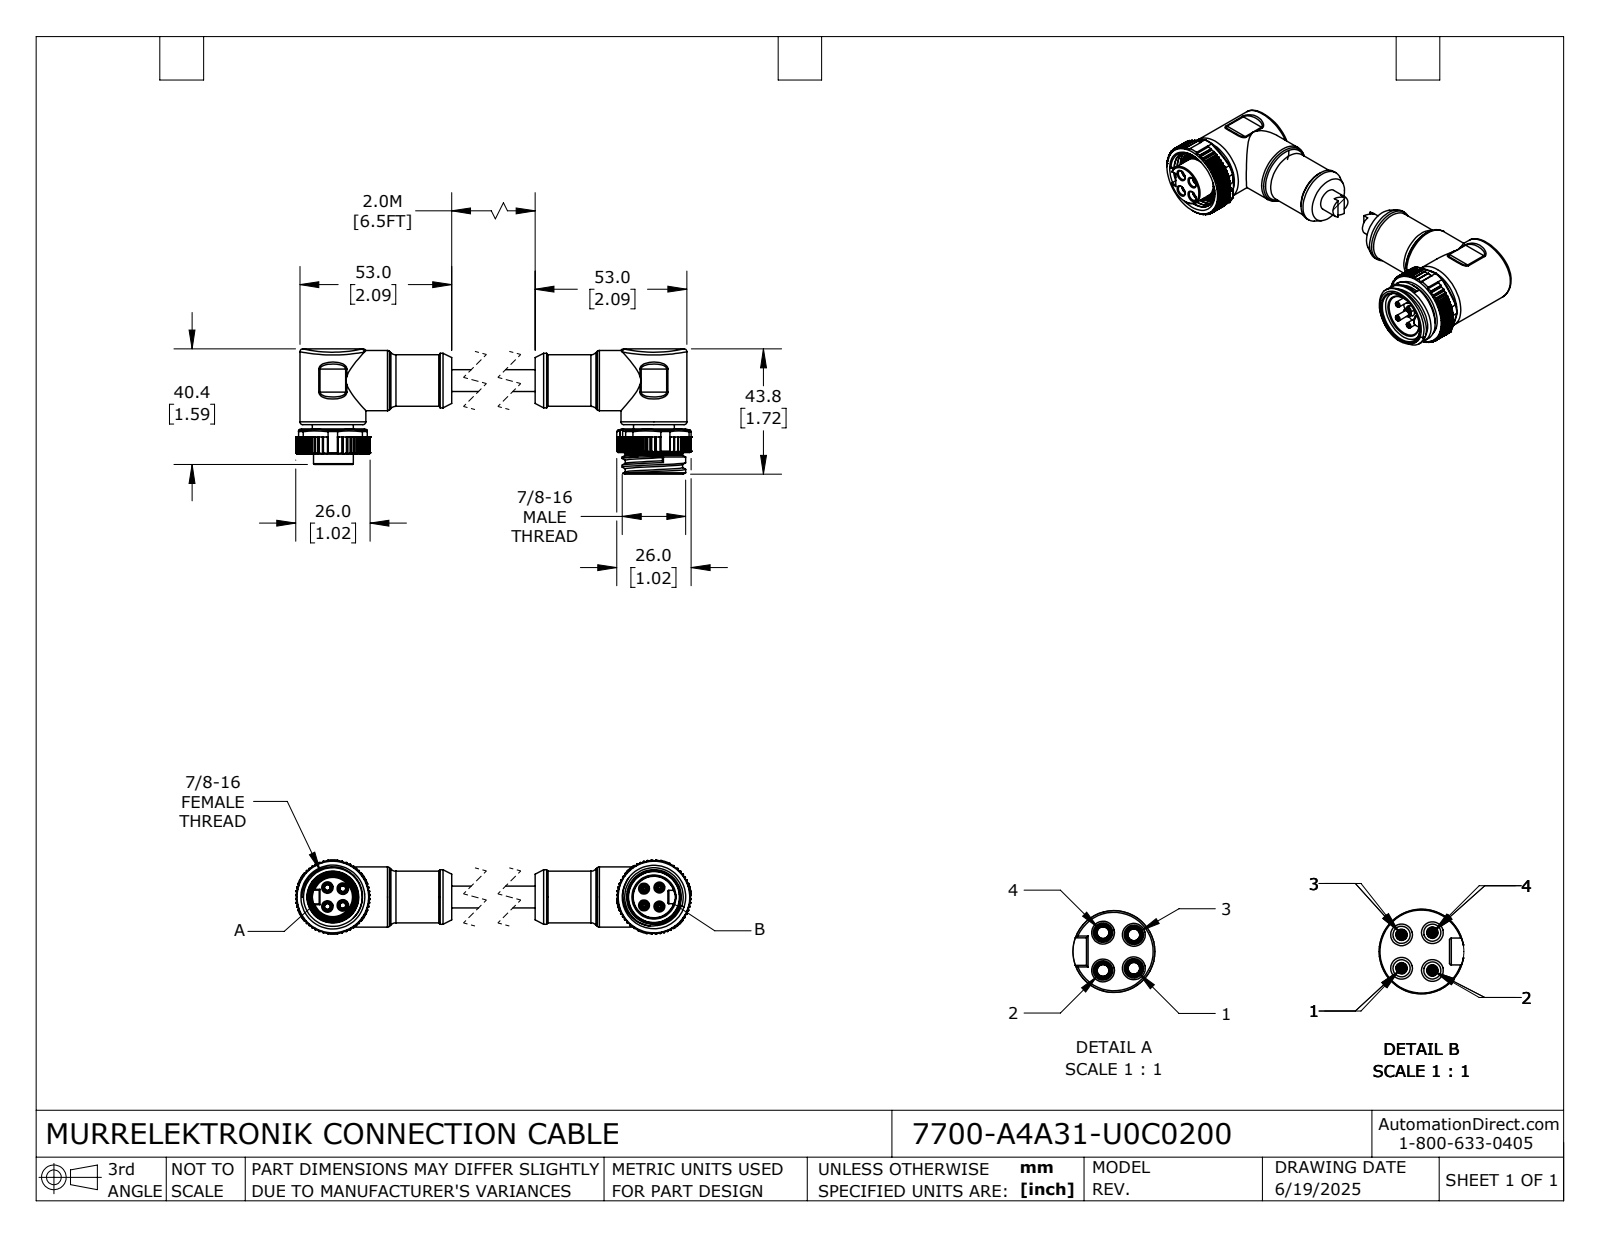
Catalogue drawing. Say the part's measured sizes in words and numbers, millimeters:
The part is named "7700-A4A31-U0C0200_MALE; 7700-A4A31-U0C0200_FEMALE; 7700-A4A31-U0C0200". Its 3-D file was written by "SolidWorks 2024 (CONFIG_CONTROL_DESIGN)". It is 2 solids with 1268 faces: 520 planar, 581 cylindrical and 167 other. Overall it measures 138.97 by 43.76 by 26 millimeters. Its volume is 49 781 cubic millimeters and its surface area 17 240 square millimeters. Round holes: 4 of diameter 2.05, 4 of diameter 3, 4 of diameter 3.4, 2 of diameter 15.6, 1 of diameter 15.5, 1 of diameter 18.5, 1 of diameter 20.5, 1 of diameter 22.22. Round bosses or shafts: 4 of diameter 3, 4 of diameter 2, 2 of diameter 23, 2 of diameter 18.1, 2 of diameter 17.8, 2 of diameter 14.3, 1 of diameter 22.17, 1 of diameter 21. Partial cylindrical surfaces (rounded edges, fillets, slot ends): 252 of radius 0.2, 34 of radius 0.3, 8 of radius 0.1, 8 of radius 1, 4 of radius 0.7, 4 of radius 0.73, 4 of radius 2.5, 2 of radius 13. The main face-to-face distances are 1.5, 8.8, 7.3, 9.7, 0.9, 7, 30, 8.2, 21, 4.2. The hole center spacings are 3.81, 4.54, 5.39, 8.22, 109.56, 114.95, 5.84, 6.6.
